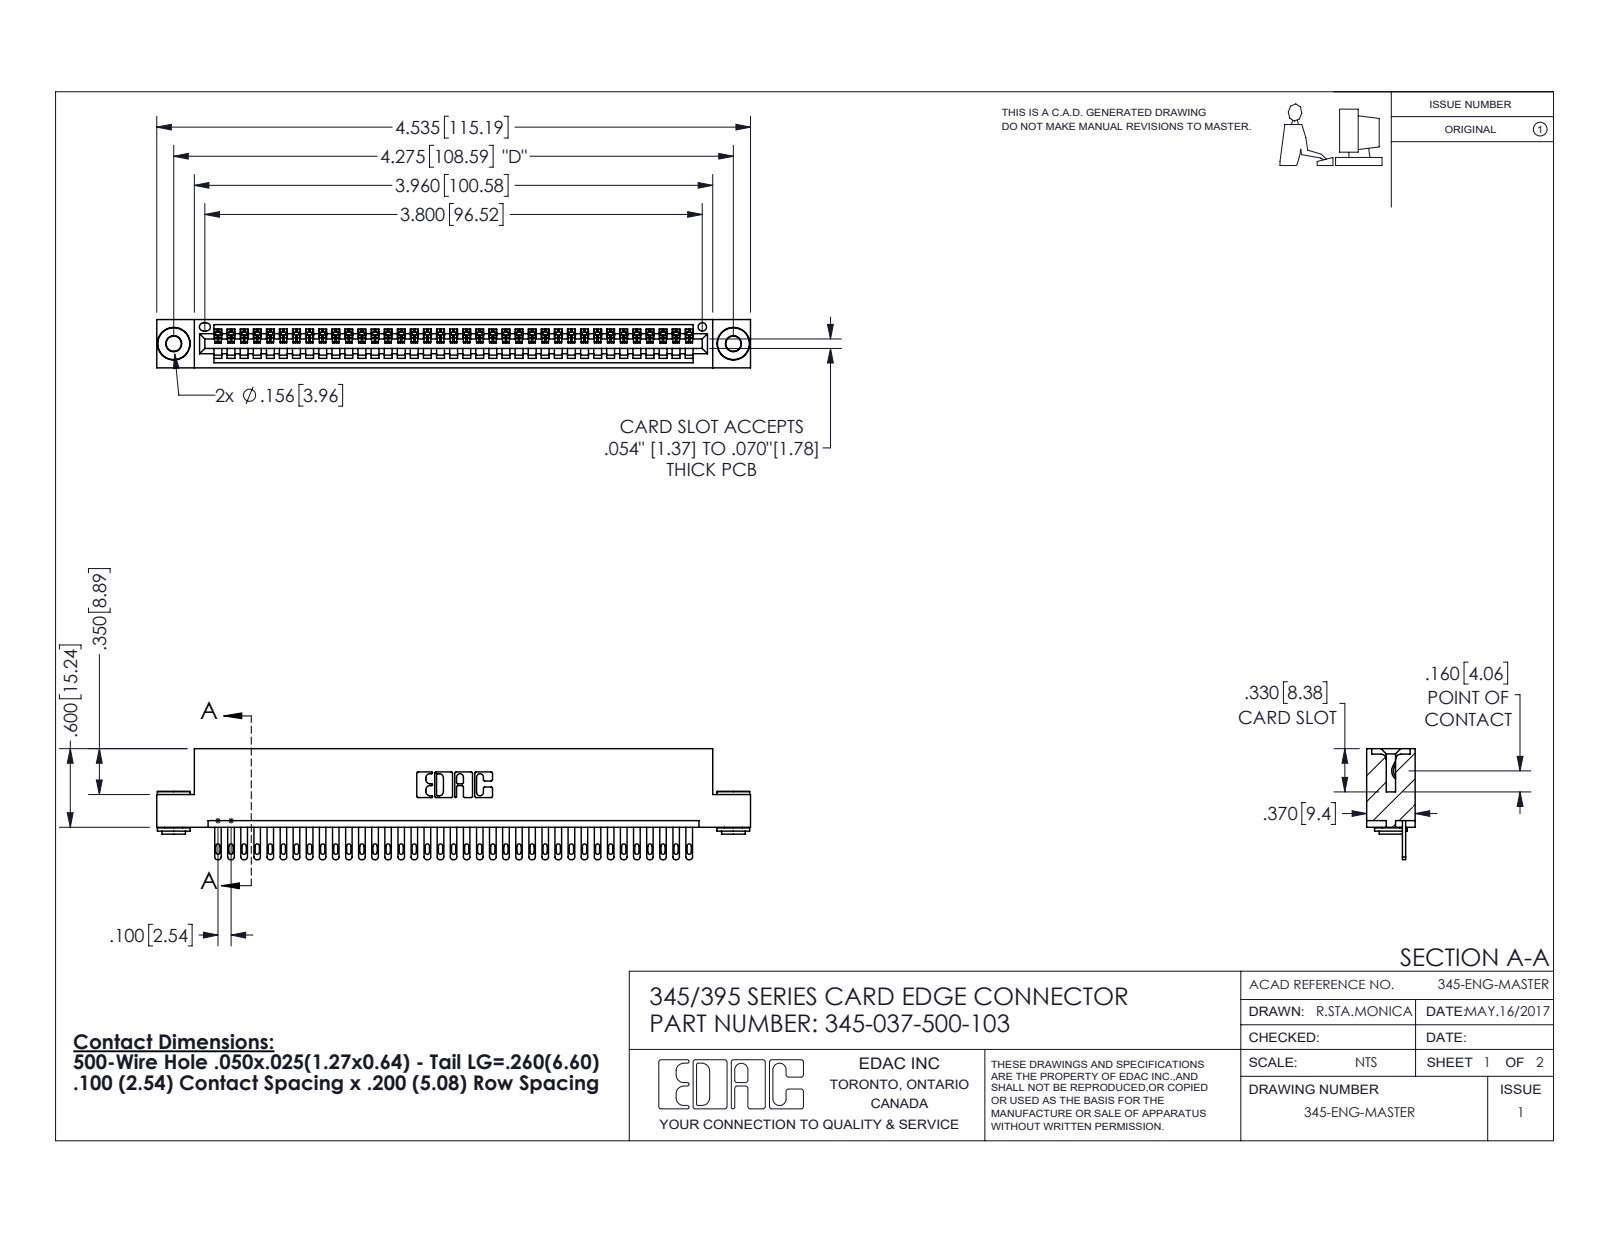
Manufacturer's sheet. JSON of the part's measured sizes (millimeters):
{"part_name": "345-292-001_345-293-100; 345-250-002_345-250-002-102; 345-037-500-103; 345 Part_Flush Mounting Lugs - 0.156 Dia-TH", "step_written_by": "SolidWorks 2016 (CONFIG_CONTROL_DESIGN)", "units": "millimeters", "bodies": {"solids": 40, "faces": 2162, "planar": 1348, "cylindrical": 806, "other": 8}, "overall_size": [115.2, 21.5, 9.4], "volume_mm3": 10900, "surface_area_mm2": 14770, "round_holes": [[2.9, 2], [4, 2], [1.6, 1]], "round_bosses_or_shafts": [[6.4, 2], [4.6, 2], [3.5, 2]], "partial_cylinders_radius": [[0.2, 74], [0.4, 74], [0.5, 74], [0.3, 22], [0.2, 6], [0.8, 6], [0.7, 3], [0.8, 2]], "face_to_face_distances": [1.8, 7.6, 5.1, 9.4, 0.6, 2.5, 6.9, 5.7, 3.8, 1.8], "hole_center_spacings": [6.9, 102.6, 108.6]}
